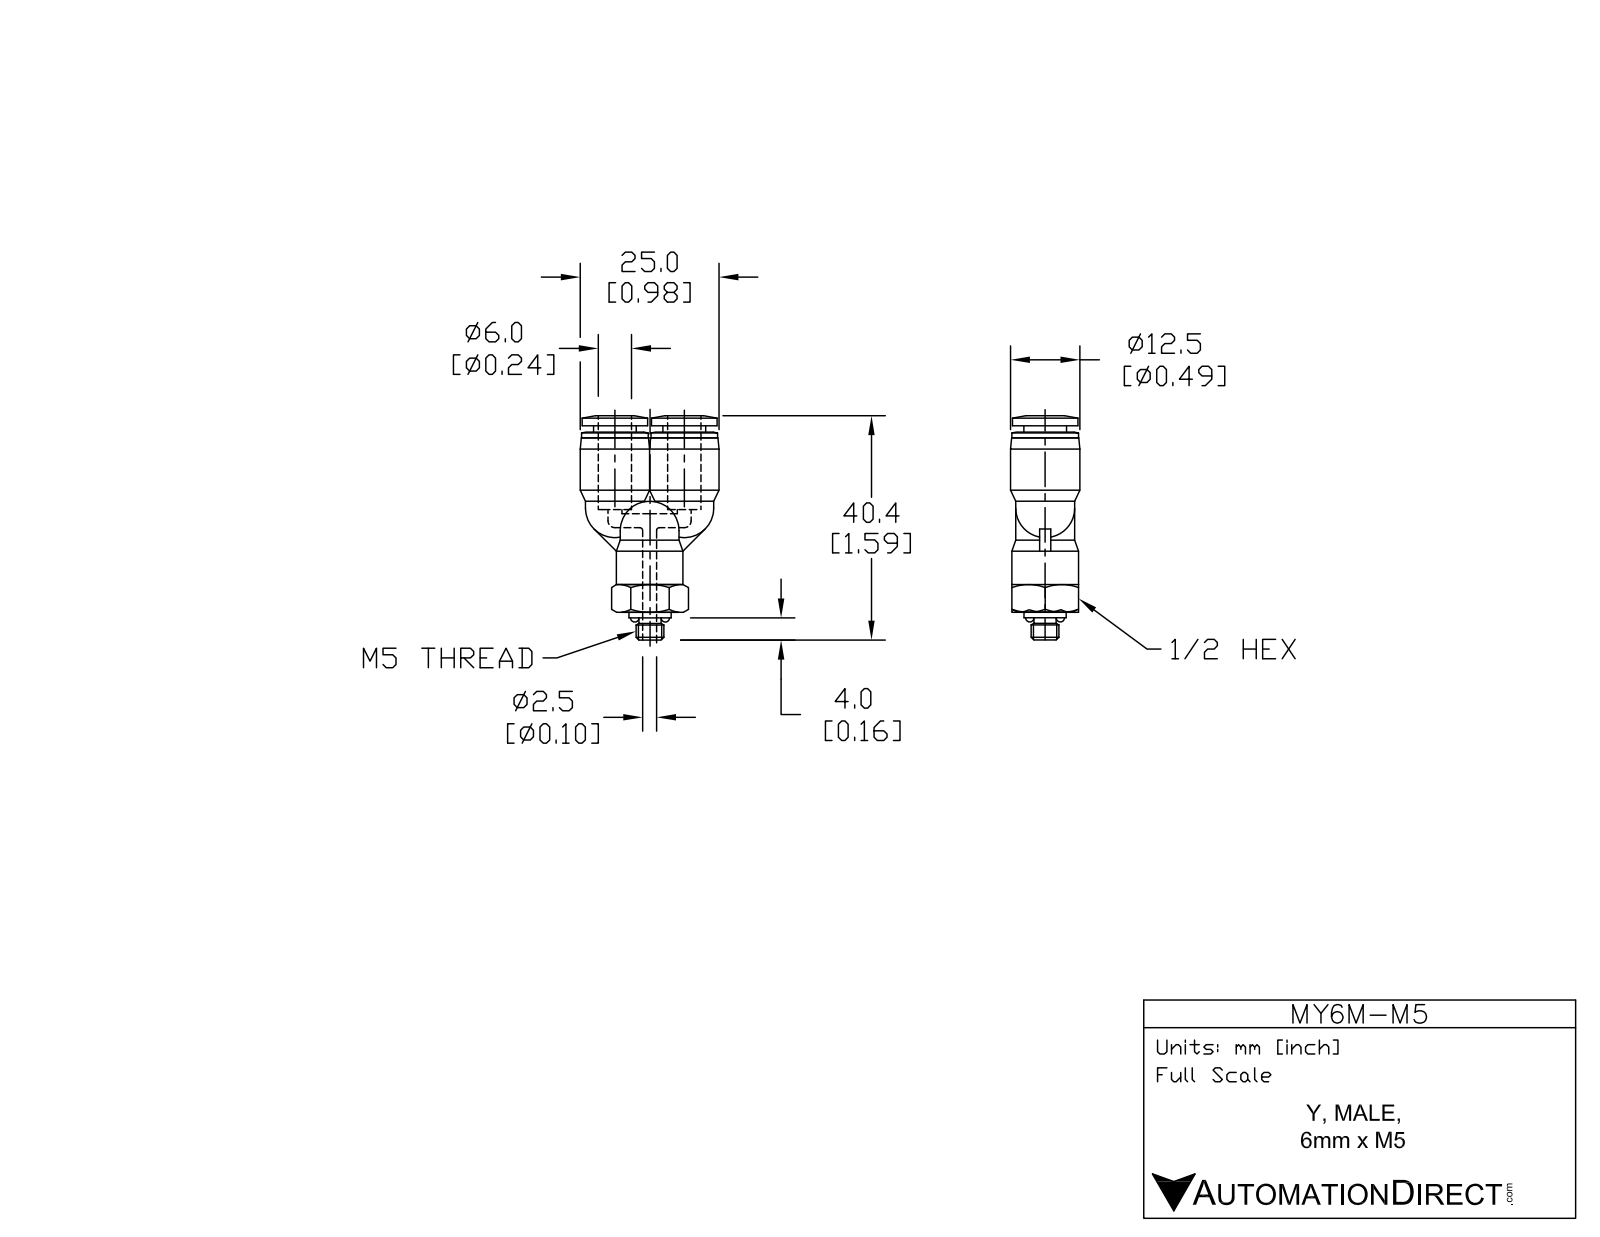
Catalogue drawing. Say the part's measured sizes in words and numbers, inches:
The part is named "MY6M-M5". Its 3-D file was written by "SolidWorks 2015 (AUTOMOTIVE_DESIGN)". It is 2 solids with 122 faces: 26 planar, 42 cylindrical and 54 other. Overall it measures 1.591 by 0.984 by 0.492 inches. Its volume is 0.303 cubic inches and its surface area 5.85 square inches. Round holes: 4 of diameter 0.098, 2 of diameter 0.248. Round bosses or shafts: 3 of diameter 0.472, 3 of diameter 0.417, 2 of diameter 0.492, 2 of diameter 0.465, 2 of diameter 0.303, 1 of diameter 0.299, 1 of diameter 0.197, 1 of diameter 0.157. The main face-to-face distances are 0.045, 0.472, 1.278, 1.323, 0.728, 0.549, 0.594, 0.197, 0.276, 0.736. The hole center spacings are 0.246, 0.492.
